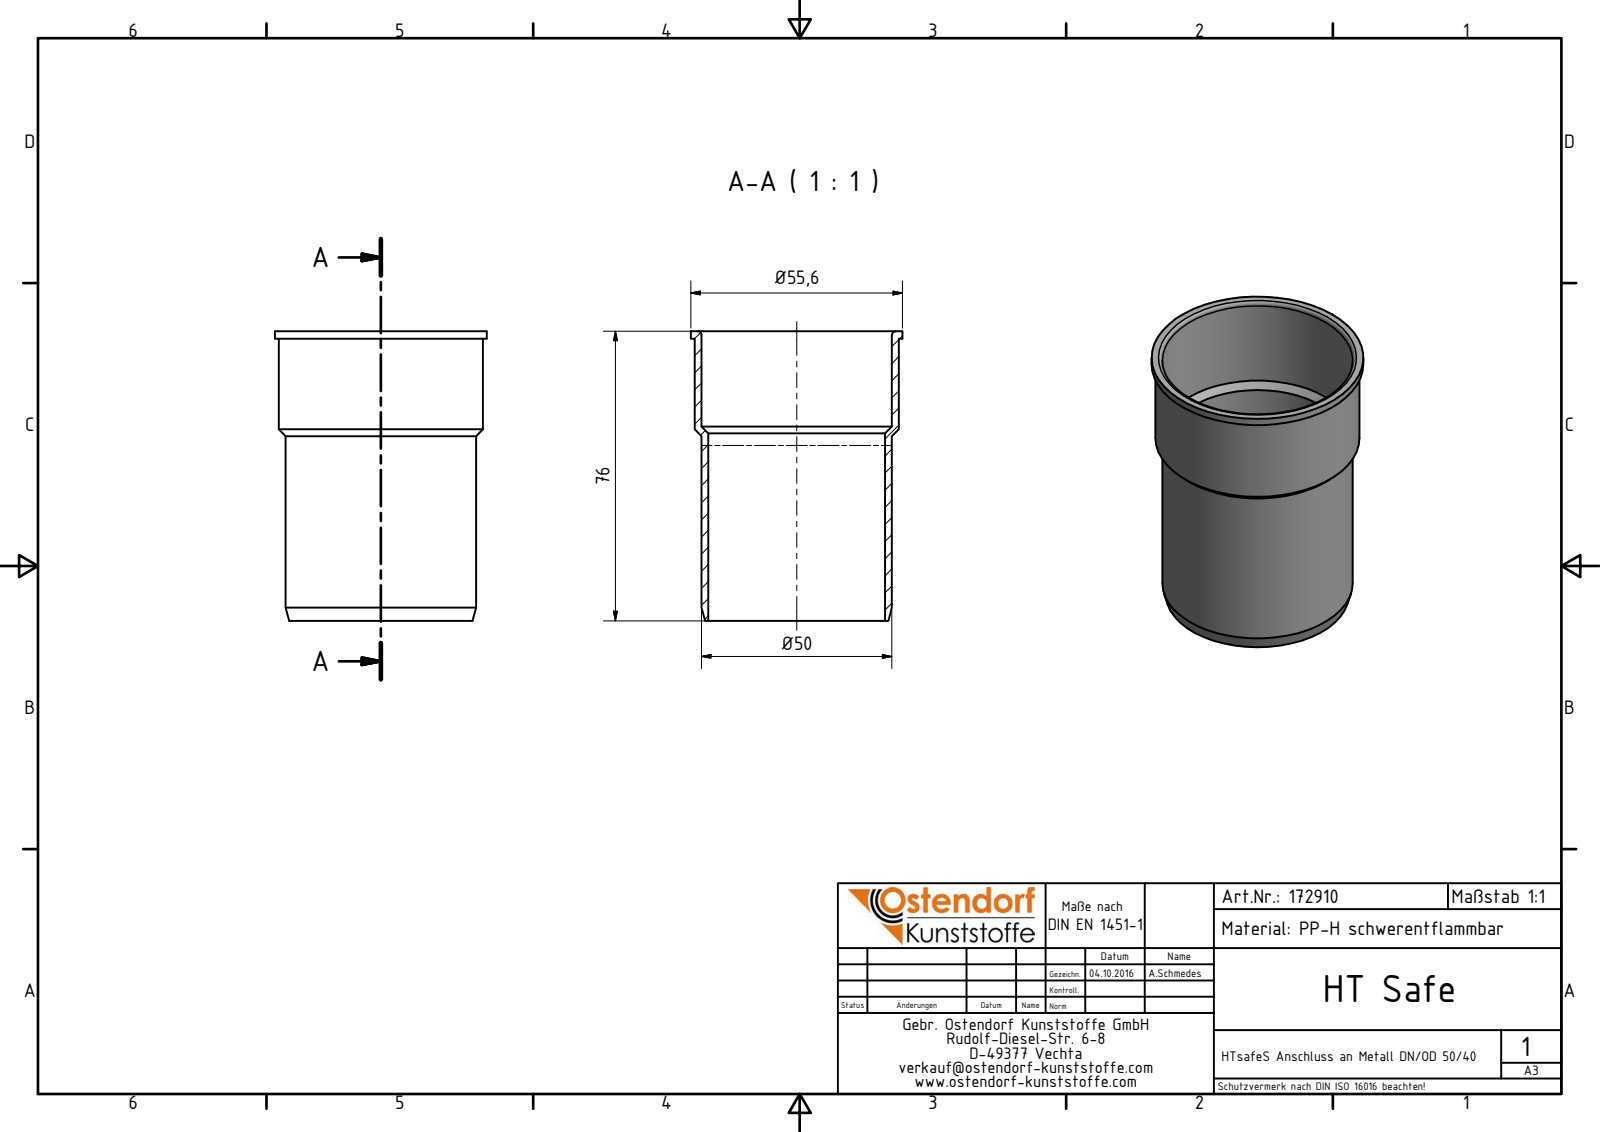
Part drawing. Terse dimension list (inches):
name: 172910 HTsafeS DN_OD 50_40
written by: Autodesk Inventor 2016 (AUTOMOTIVE_DESIGN)
unit: in
bodies: 1 solid, 12 faces (3 planar, 5 cylindrical, 4 other)
size: 2.992 × 2.189 × 2.189
volume: 1.313 in³; area: 38.07 in²
holes: 1× ⌀1.827, 1× ⌀1.969
bosses: 1× ⌀2.189, 1× ⌀2.11
face distances: 0.079, 2.913, 2.992
